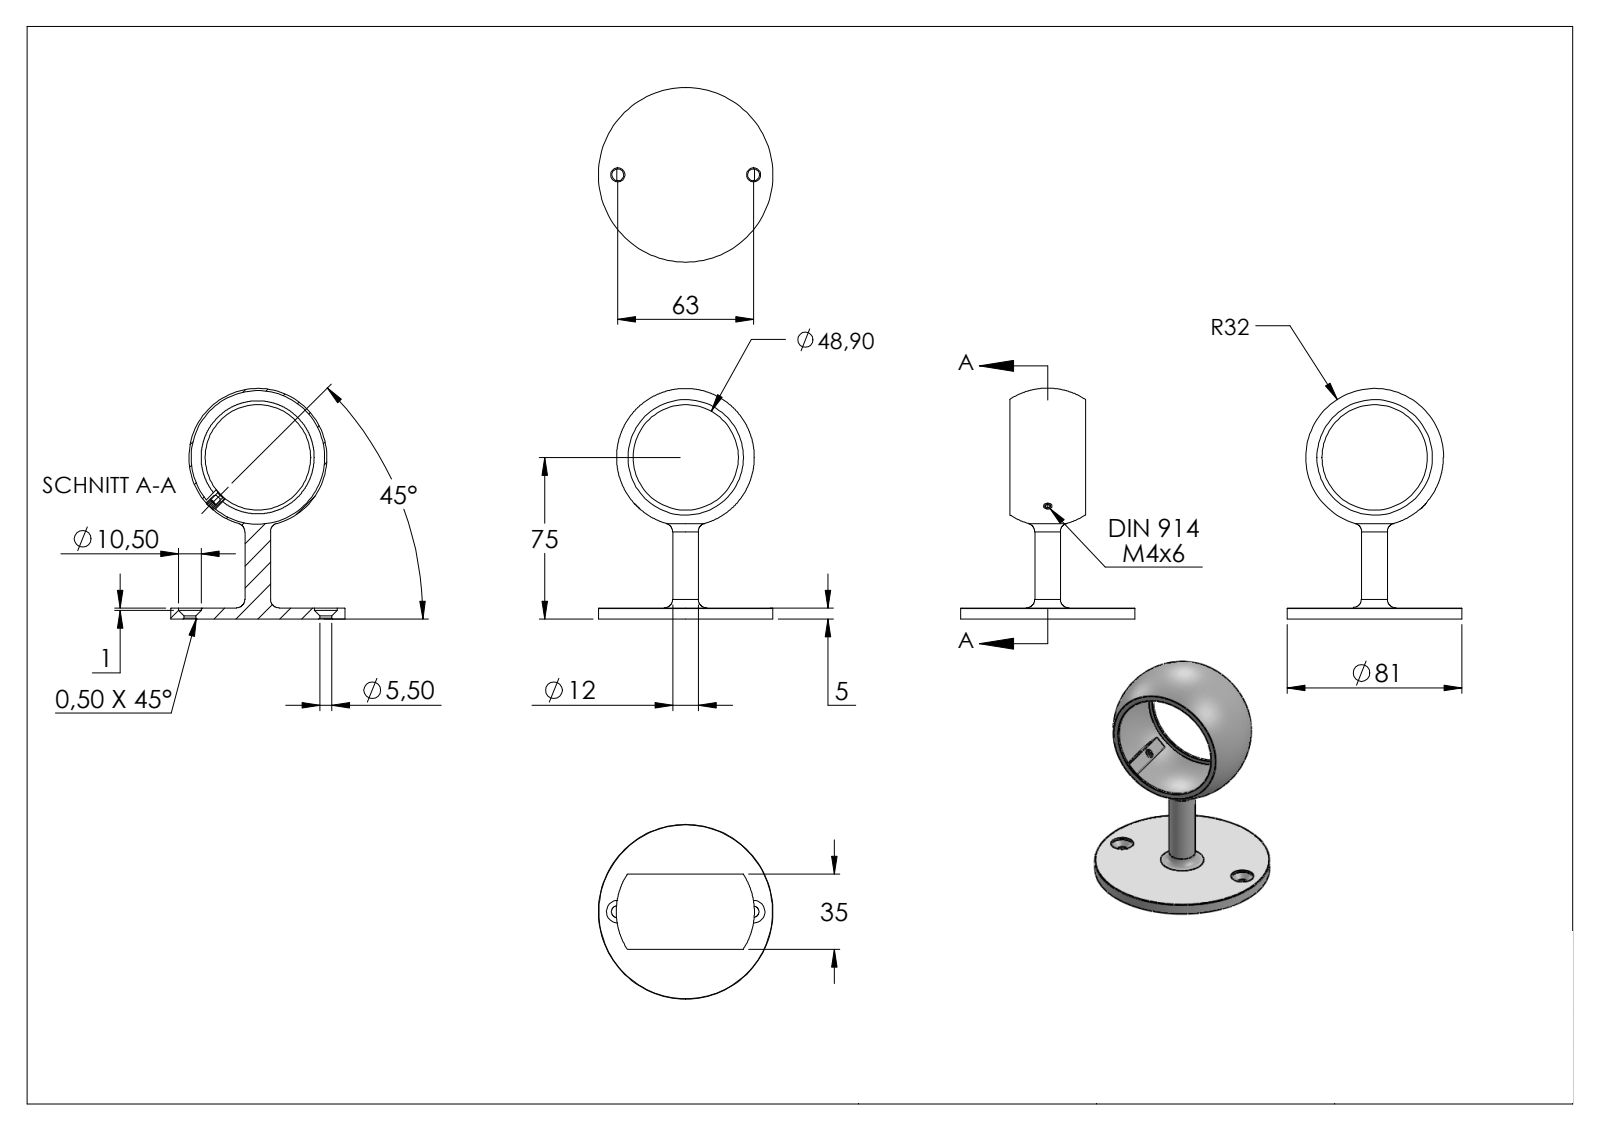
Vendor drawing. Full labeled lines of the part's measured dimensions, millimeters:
Part name (STEP PRODUCT): 7011X-XX Konfig_70111-ME; DIN913_DIN 913 M4x6; 70111-ME
STEP written by: SolidWorks 2018 (CONFIG_CONTROL_DESIGN)
Units: millimetres
Bodies: 2 solids, 232 faces (151 planar, 10 cylindrical, 71 other)
Overall size (bounding box): 107 × 81 × 81
Volume: 38 085 mm³ · Surface area: 28 324 mm²
Round holes (diameter × count): ⌀5.5 ×2, ⌀10.5 ×2, ⌀3.3 ×1, ⌀48.9 ×1
Round bosses / shafts (diameter × count): ⌀81 ×1, ⌀12 ×1, ⌀4 ×1
Main face-to-face distances: 5, 1, 34, 35, 33, 5.99, 6, 28, 29, 2
Hole centre spacings: 63
